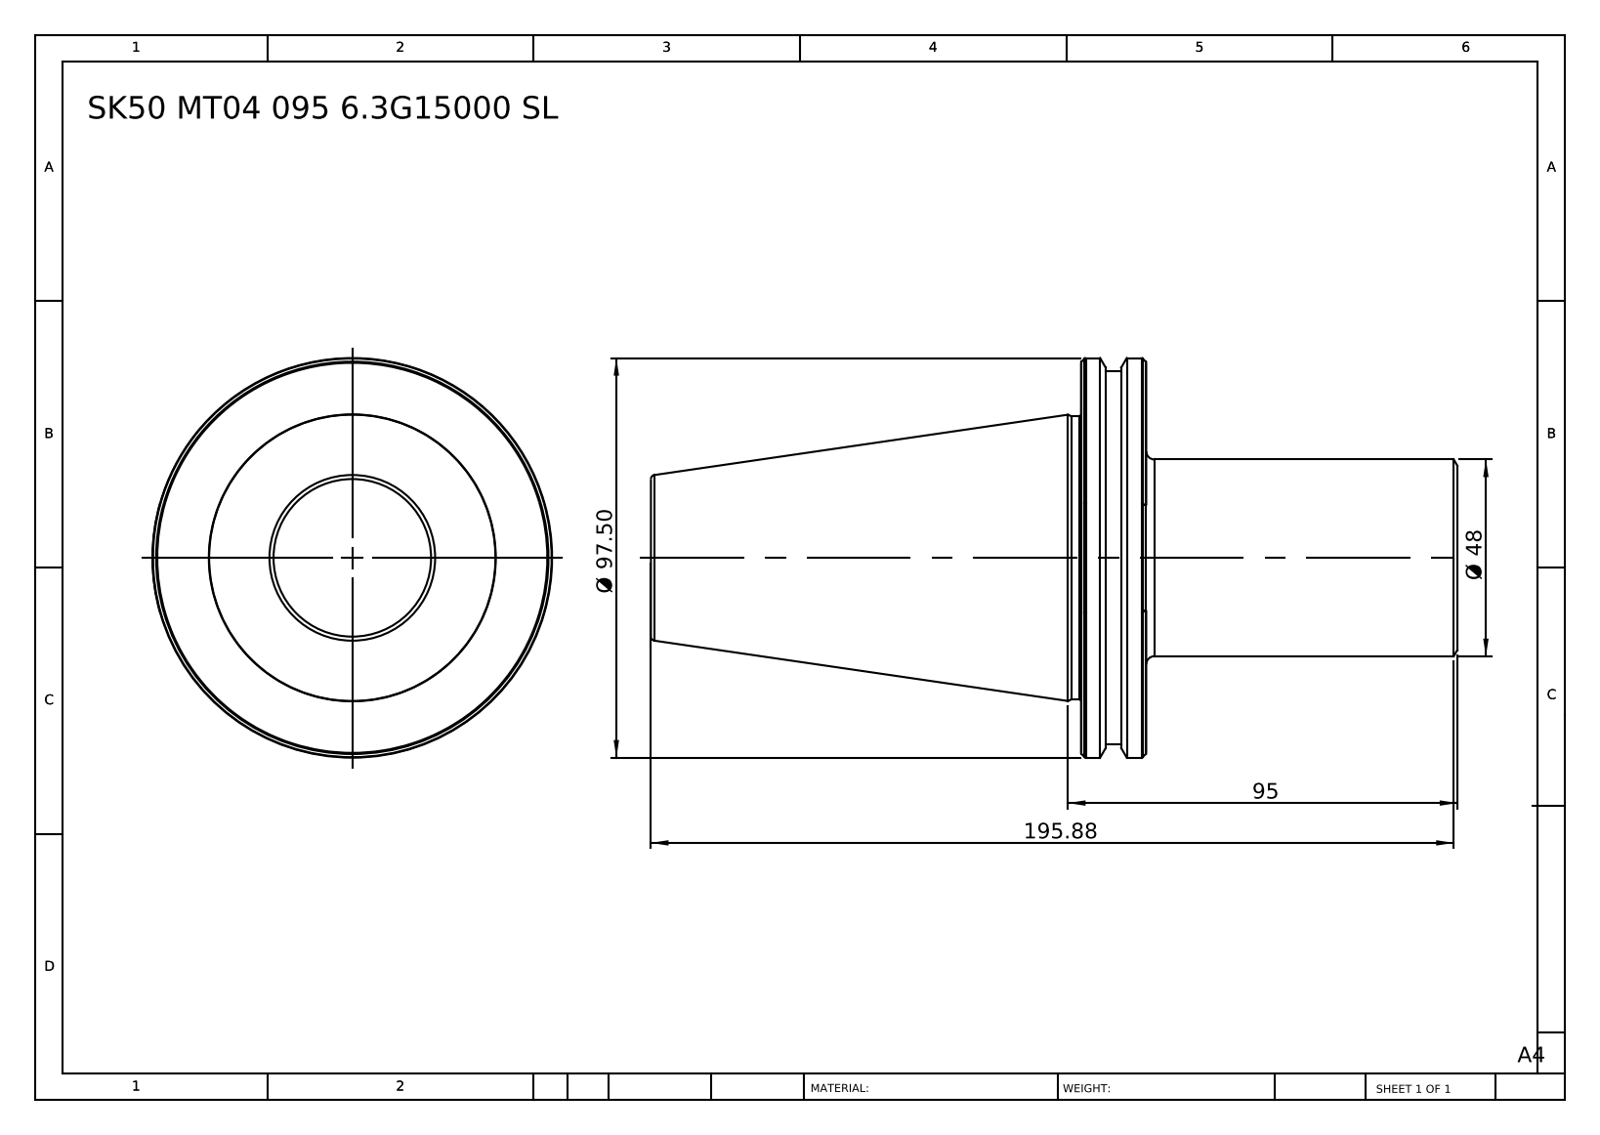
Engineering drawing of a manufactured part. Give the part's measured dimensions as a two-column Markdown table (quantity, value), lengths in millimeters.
| quantity | value |
| --- | --- |
| part name | SK 50 MT04 095 6.3G15000 SL |
| STEP written by | SolidWorks 2014 (CONFIG_CONTROL_DESIGN) |
| units | millimeters |
| bodies | 1 solid, 69 faces (6 planar, 10 cylindrical, 53 other) |
| overall size | 196.75 × 97.5 × 97.5 |
| volume | 510 892 mm³ |
| surface area | 47 808 mm² |
| round bosses / shafts (diameter × count) | 97.5 × 1, 91 × 1, 69 × 1, 48 × 1 |
| main face-to-face distances | 15.9, 75.9, 91.8, 196.75, 120.85, 104.95, 82, 6.1, 9.8, 114.75 |
